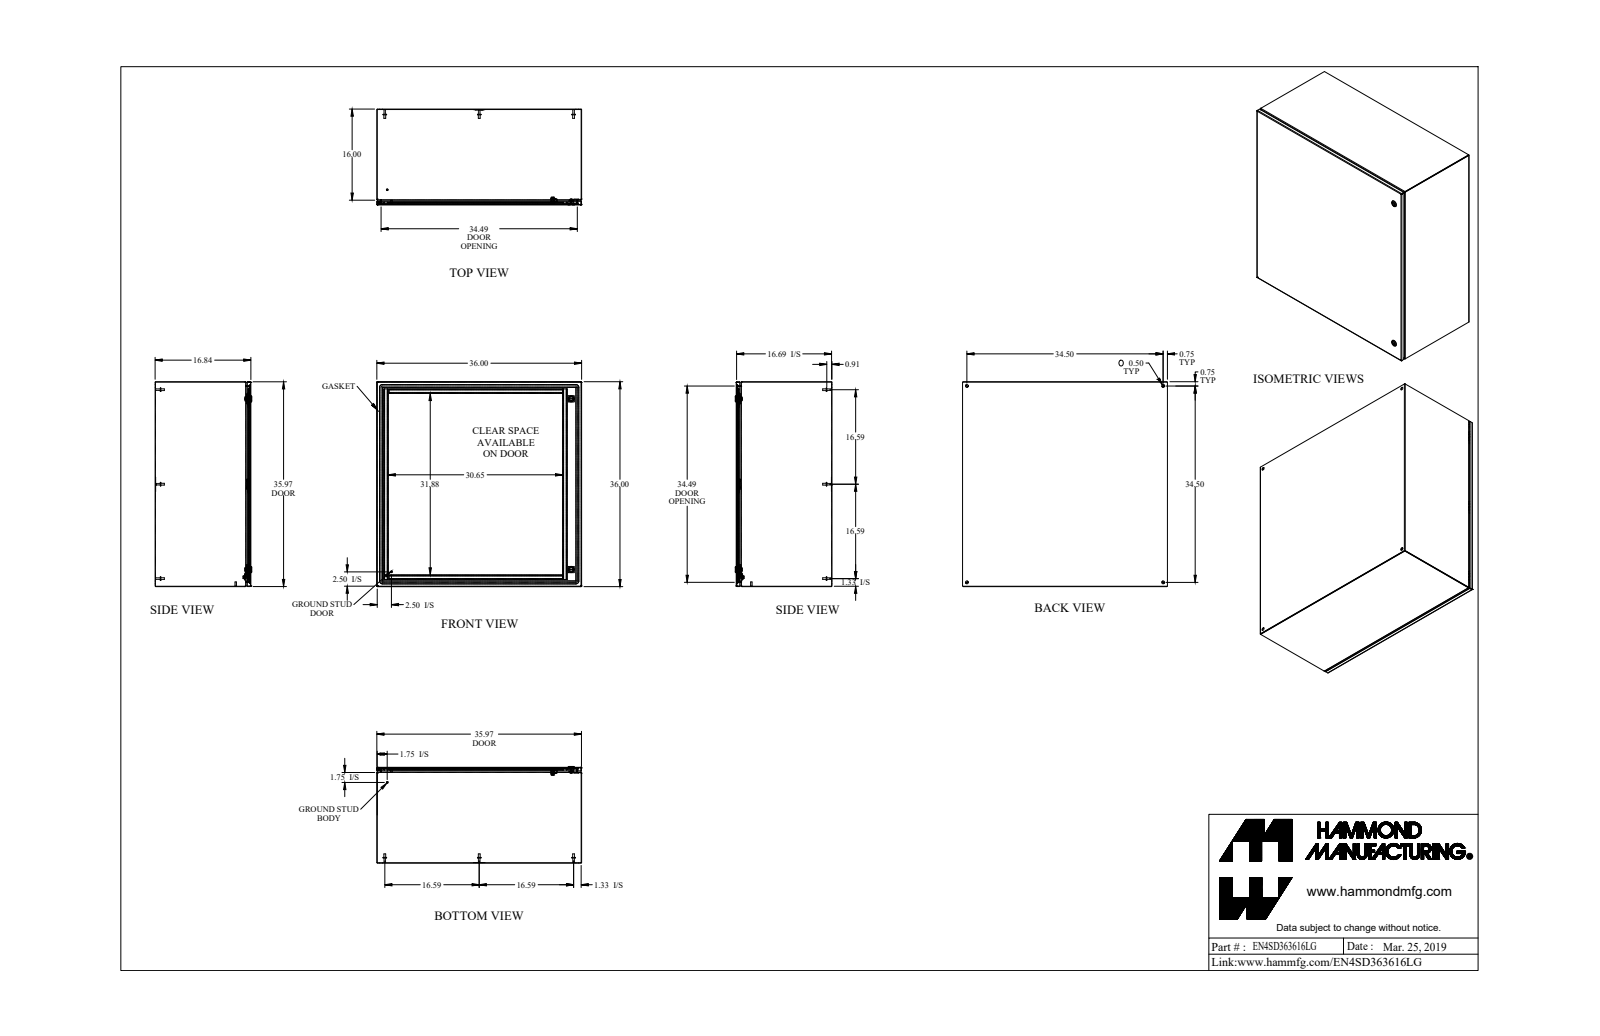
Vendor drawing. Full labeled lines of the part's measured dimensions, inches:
Part name (STEP PRODUCT): EN4SD363616LG
STEP written by: SolidWorks 2019 (AUTOMOTIVE_DESIGN)
Units: inches
Bodies: 43 solids, 1177 faces (559 planar, 395 cylindrical, 223 other)
Overall size (bounding box): 36 × 36 × 16.997
Volume: 396.2 in³ · Surface area: 11 179 in²
Round holes (diameter × count): ⌀0.5 ×4, ⌀0.232 ×2, ⌀0.625 ×2, ⌀0.785 ×2, ⌀0.172 ×1, ⌀0.196 ×1, ⌀0.24 ×1, ⌀0.242 ×1, ⌀0.275 ×1, ⌀0.375 ×1
Round bosses / shafts (diameter × count): ⌀0.313 ×8, ⌀0.27 ×8, ⌀0.625 ×6, ⌀0.625 ×3, ⌀1.1 ×2, ⌀0.525 ×2, ⌀0.281 ×2, ⌀0.25 ×2
Partial cylindrical surfaces — rounded edges, fillets, slot ends (radius × count): R0.043 ×24, R0.081 ×24, R0.036 ×18, R0.108 ×18, R0.312 ×12, R0.062 ×10, R0.094 ×10, R0.016 ×9
Main face-to-face distances: 0.072, 16.765, 35.928, 16.693, 16.837, 35.856, 36, 0.837, 15.928, 0.038
Hole centre spacings: 34.5, 33.502, 48.791, 2.493, 2.494, 3.542, 4.442, 29.999
